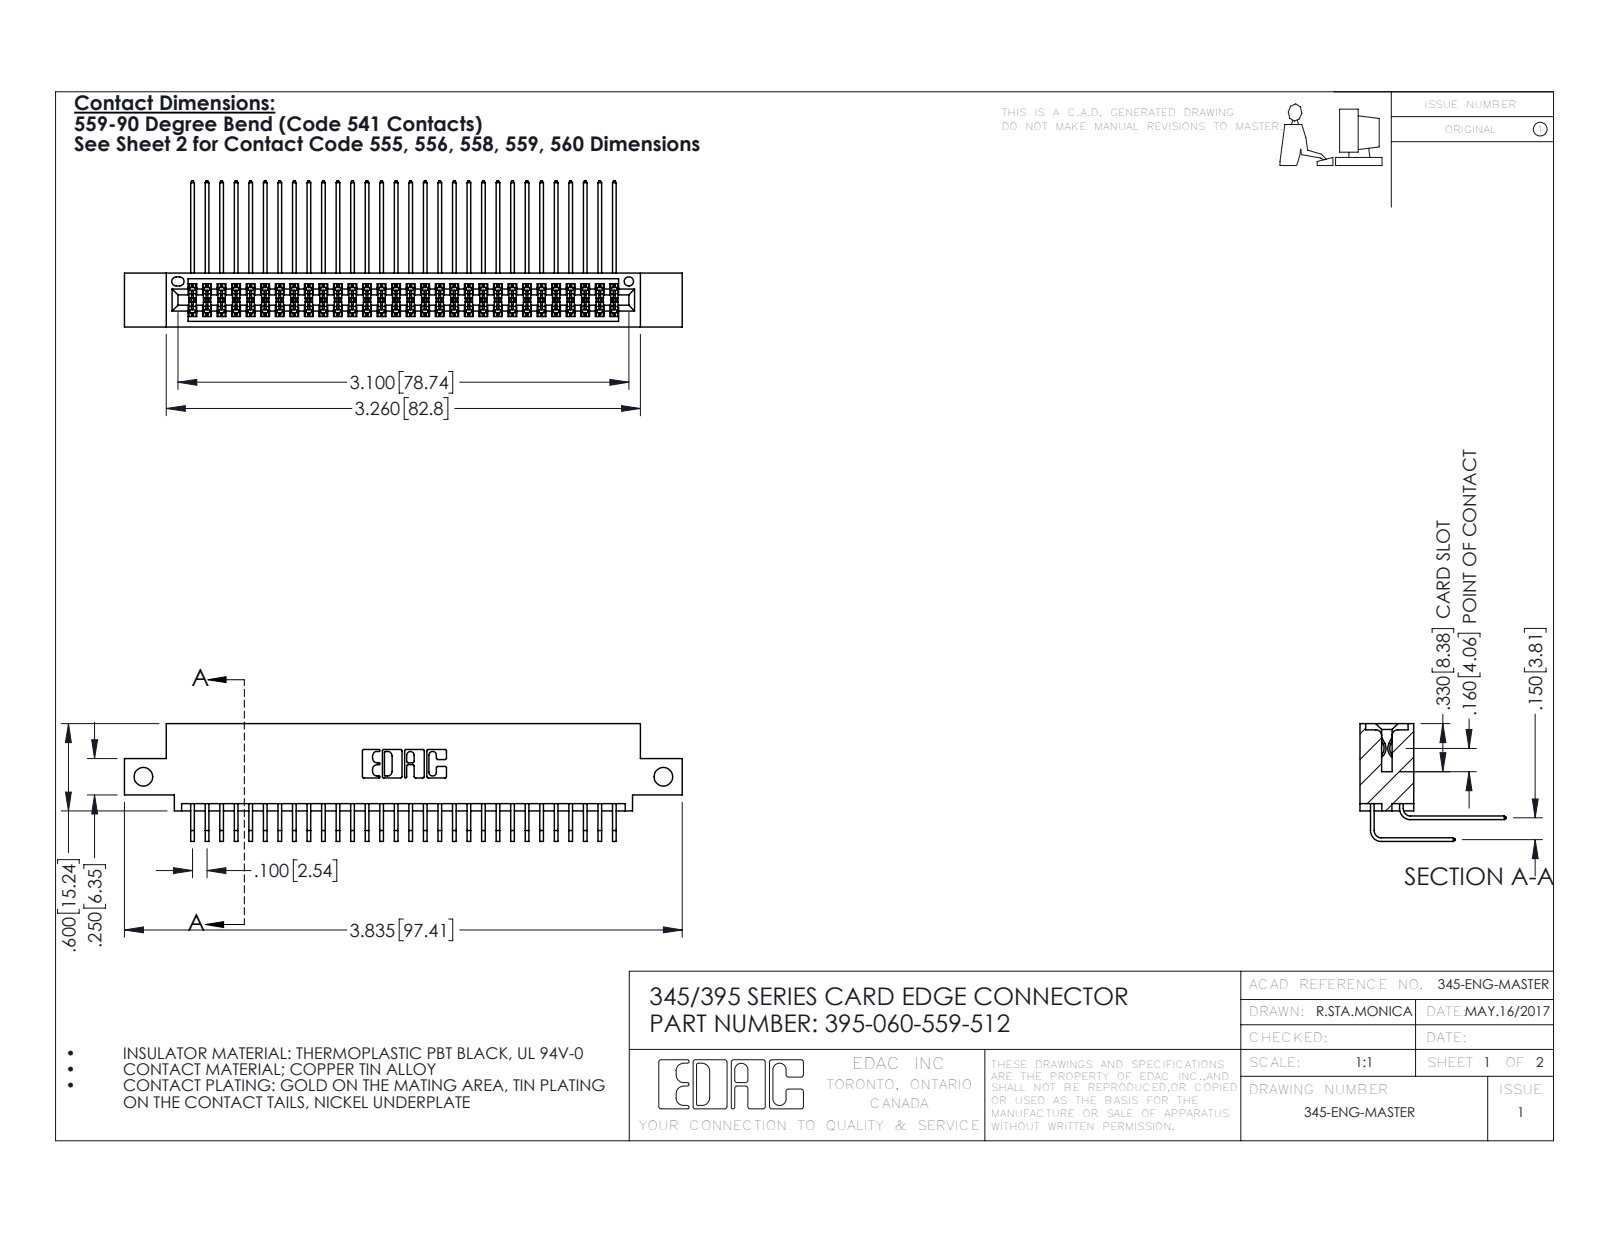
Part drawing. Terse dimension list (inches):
name: 345-292-001_558 559 Tail - 1; 345-292-001_559 Tail - 2; 395-060-559-512; 345 Part_0.110 Offset - Side Mount
written by: SolidWorks 2016 (CONFIG_CONTROL_DESIGN)
unit: in
bodies: 61 solids, 3250 faces (2184 planar, 1066 cylindrical, 0 other)
size: 3.835 × 1.005 × 0.809
volume: 0.582 in³; area: 23.95 in²
holes: 2× ⌀0.128, 1× ⌀0.064
rounds: 90× R0.006, 22× R0.01, 6× R0.007, 6× R0.031, 3× R0.026, 2× R0.014, 2× R0.019, 2× R0.022
face distances: 0.072, 0.298, 0.2, 0.37, 0.098, 0.272, 0.025, 0.225, 0.15, 0.175
hole spacings: 3.575
